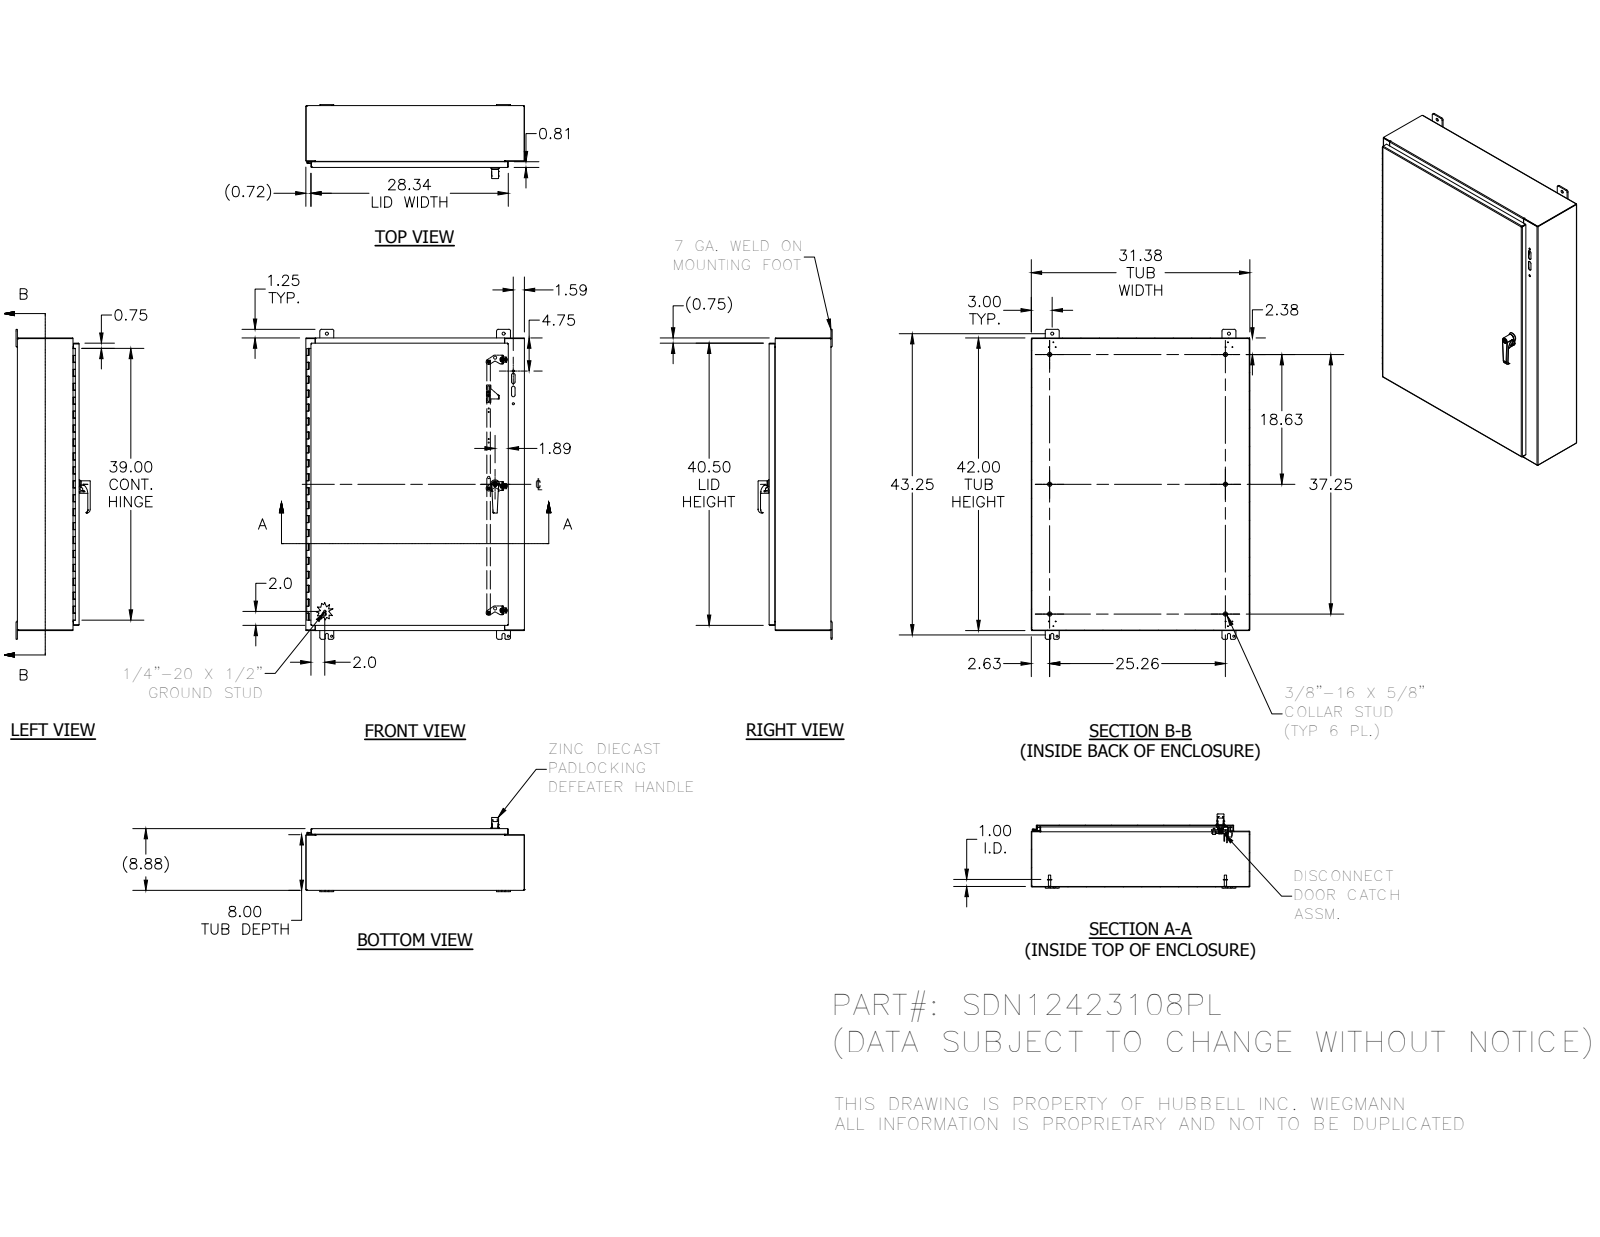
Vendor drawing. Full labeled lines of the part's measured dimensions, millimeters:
Part name (STEP PRODUCT): SDN12423108PL; SDN12423108PLBKP; 388116; 34840 (+8 more)
STEP written by: Autodesk Inventor 2012 (AUTOMOTIVE_DESIGN)
Units: millimetres
Bodies: 60 solids, 1883 faces (978 planar, 643 cylindrical, 262 other)
Overall size (bounding box): 1130.3 × 797.1 × 270.5
Volume: 5 237 000 mm³ · Surface area: 5 514 000 mm²
Round holes (diameter × count): ⌀3 ×12, ⌀3.7 ×6, ⌀8 ×4, ⌀8.1 ×4, ⌀11.1 ×4, ⌀5 ×3, ⌀5.4 ×3, ⌀5.6 ×3, ⌀8 ×3, ⌀11.4 ×3, ⌀4 ×2, ⌀7.1 ×2
Round bosses / shafts (diameter × count): ⌀15.9 ×8, ⌀8.4 ×8, ⌀11.1 ×6, ⌀7.6 ×6, ⌀5.7 ×6, ⌀6.4 ×4, ⌀4.8 ×4, ⌀19.1 ×3
Partial cylindrical surfaces — rounded edges, fillets, slot ends (radius × count): R0.5 ×38, R0.3 ×30, R0.6 ×24, R6.4 ×23, R3.2 ×21, R0.8 ×20, R2.7 ×20, R1.8 ×8
Main face-to-face distances: 1.9, 223.5, 221.7, 225.4, 795.2, 1064.9, 201.3, 22.2, 793.3, 797.1
Hole centre spacings: 453.2, 461.2, 19.3, 628.5, 644.7, 914.4, 1000.3, 1000.6
